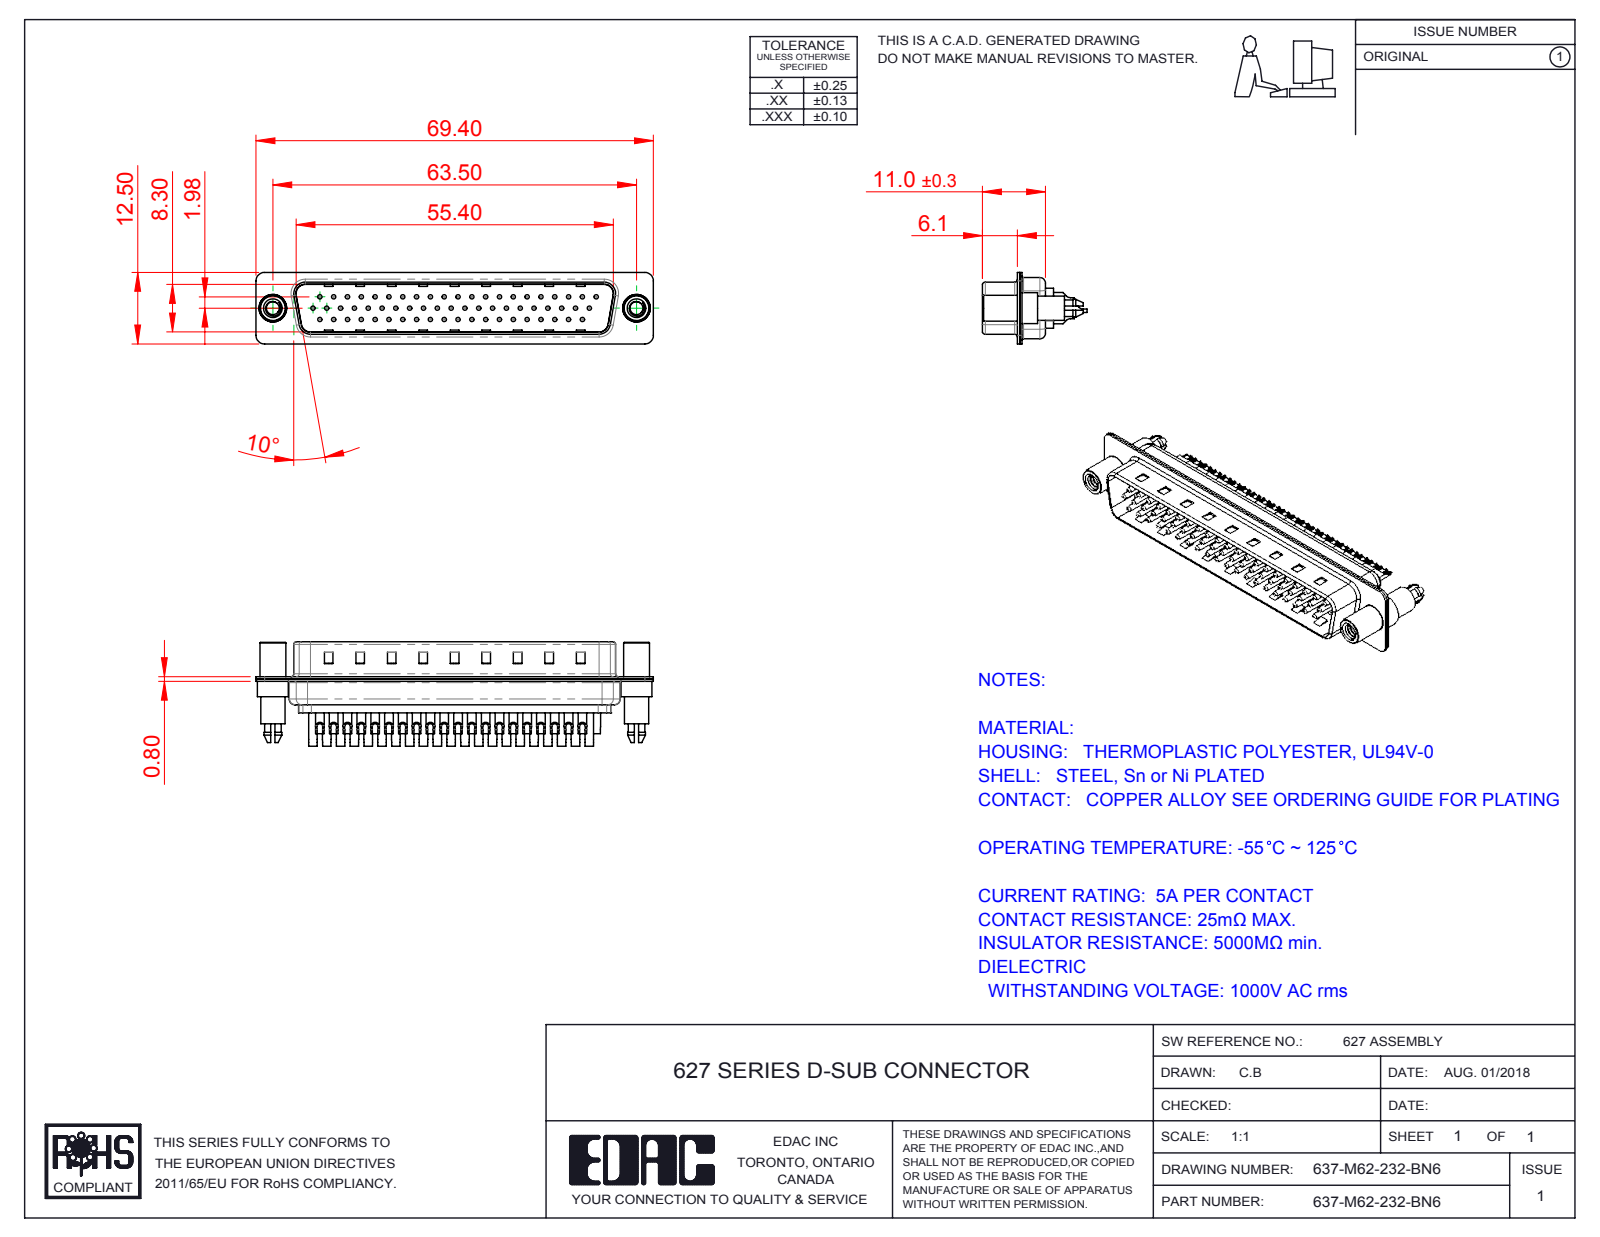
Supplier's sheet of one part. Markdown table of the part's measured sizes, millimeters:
| quantity | value |
| --- | --- |
| part name | 637M Contact Row 1_32; 637M Contact Row 3_32; 637M 4-40 Threaded Standoff and Boardlock; 637M Shell Rear_62 Contacts (+4 more) |
| STEP written by | SolidWorks 2016 (CONFIG_CONTROL_DESIGN) |
| units | millimeters |
| bodies | 67 solids, 2790 faces (799 planar, 1169 cylindrical, 822 other) |
| overall size | 69.4 × 18.25 × 12.5 |
| volume | 4 459 mm³ |
| surface area | 12 662 mm² |
| round holes (diameter × count) | 0.75 × 62, 1 × 62, 1.6 × 62, 2 × 62, 2.26 × 2, 4 × 2, 4.8 × 2 |
| round bosses / shafts (diameter × count) | 1.5 × 62, 5.4 × 2, 4.9 × 2, 4.5 × 2, 4.25 × 2 |
| partial cylindrical surfaces (radius × count) | 1.5 × 18, 2 × 12, 1.6 × 10, 0.5 × 8, 1 × 7, 0.25 × 4, 0.6 × 4, 0.65 × 4 |
| main face-to-face distances | 0.4, 0.8, 9.5, 9.1, 8.7, 9.9, 0.75, 0.35, 1.2, 10.3 |
| hole center spacings | 7.24, 2.32, 2.41, 4.13, 9.65, 4.83, 14.48, 11.04 |
